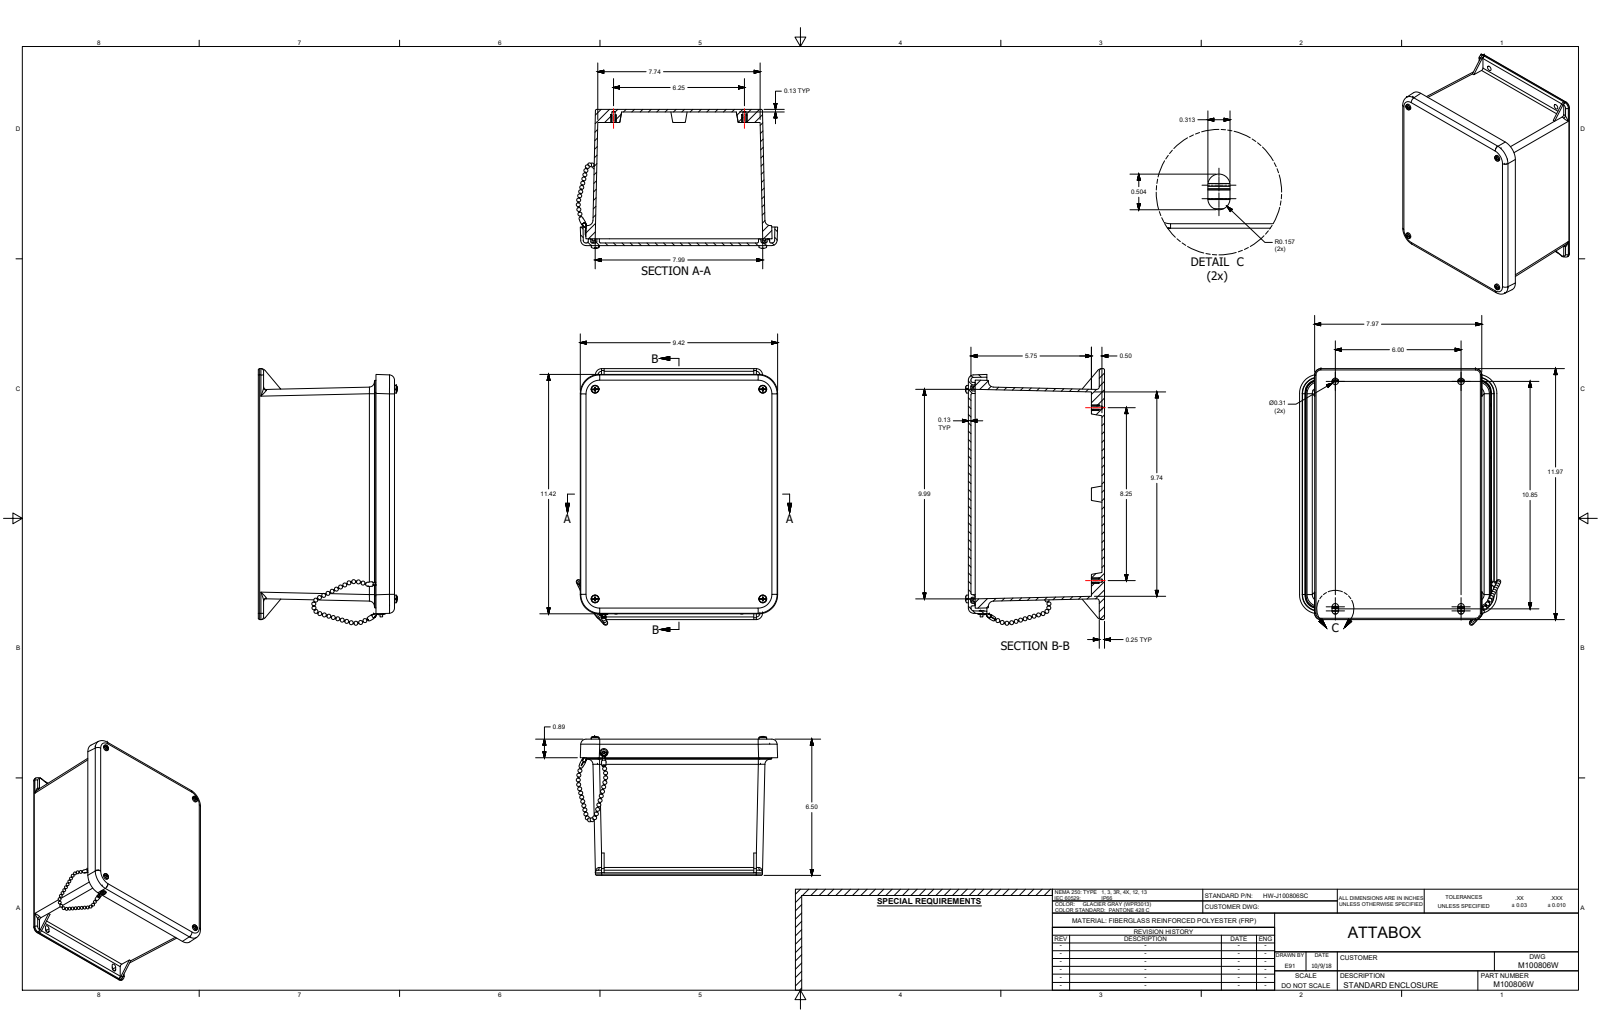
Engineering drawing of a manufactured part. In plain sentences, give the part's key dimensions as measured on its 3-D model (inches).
The part is named "M100806W". Its 3-D file was written by "SolidWorks 2018 (AUTOMOTIVE_DESIGN)". It is 54 solids with 1327 faces: 334 planar, 430 cylindrical and 563 other. Overall it measures 12.135 by 9.521 by 6.628 inches. Its volume is 76.03 cubic inches and its surface area 989.2 square inches. Round holes: 12 of diameter 0.152, 12 of diameter 0.159, 5 of diameter 0.14, 4 of diameter 0.375, 3 of diameter 0.187, 2 of diameter 0.104, 2 of diameter 0.313, 1 of diameter 0.126. Round bosses or shafts: 12 of diameter 0.27, 4 of diameter 0.19, 4 of diameter 0.156, 2 of diameter 0.375, 1 of diameter 0.375, 1 of diameter 0.283, 1 of diameter 0.125, 1 of diameter 0.125. Partial cylindrical surfaces (rounded edges, fillets, slot ends): 26 of radius 0.031, 20 of radius 0.063, 20 of radius 0.063, 18 of radius 0.125, 16 of radius 0.039, 15 of radius 0.062, 12 of radius 0.3, 10 of radius 0.25. The main face-to-face distances are 0.125, 6.497, 0.122, 0.123, 6.372, 6.247, 0.125, 6.372, 0.2, 6.172. The hole center spacings are 6, 8.704, 1.068, 1.237, 1.256, 2.5, 3.251, 4.095.
